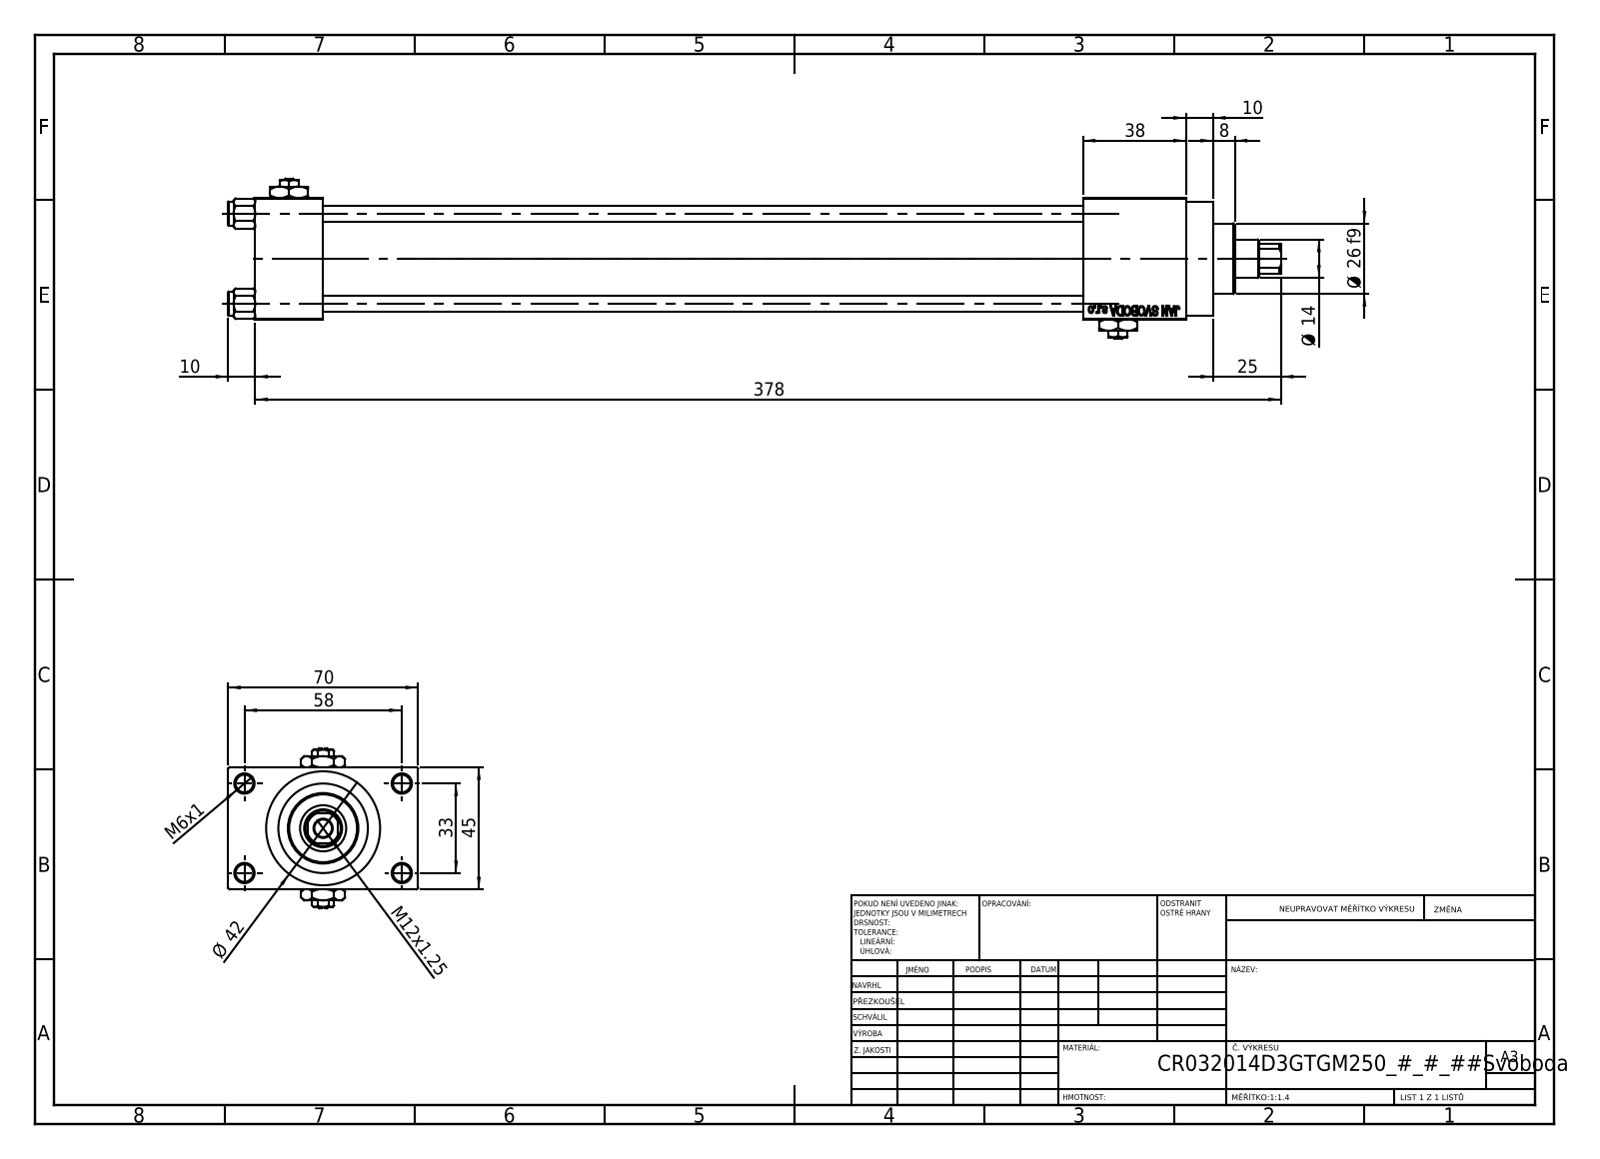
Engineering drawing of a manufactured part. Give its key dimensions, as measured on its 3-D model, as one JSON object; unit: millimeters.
{"part_name": "NUT_M5_D; Zatka_pro_OIL_PORT; V215CR_D_Body; V215CR_D_TYCINKA (+2 more)", "step_written_by": "SolidWorks 2019 (CONFIG_CONTROL_DESIGN)", "units": "millimeters", "bodies": {"solids": 13, "faces": 1187, "planar": 540, "cylindrical": 89, "other": 558}, "overall_size": [388, 70, 59], "volume_mm3": 370874, "surface_area_mm2": 154101, "round_holes": [[6.5, 5], [6, 4], [7, 2], [13.16, 2], [20, 2], [14, 1], [17, 1], [24, 1], [32, 1], [33, 1]], "round_bosses_or_shafts": [[9, 4], [42, 1], [38, 1], [26, 1]], "partial_cylinders_radius": [[6.5, 1]], "face_to_face_distances": [45, 25, 12.5, 57.5, 280, 305, 318, 70, 38, 343], "hole_center_spacings": [12.4, 23.48, 33.2, 33.37, 35.35, 45.6, 56.35, 33]}
